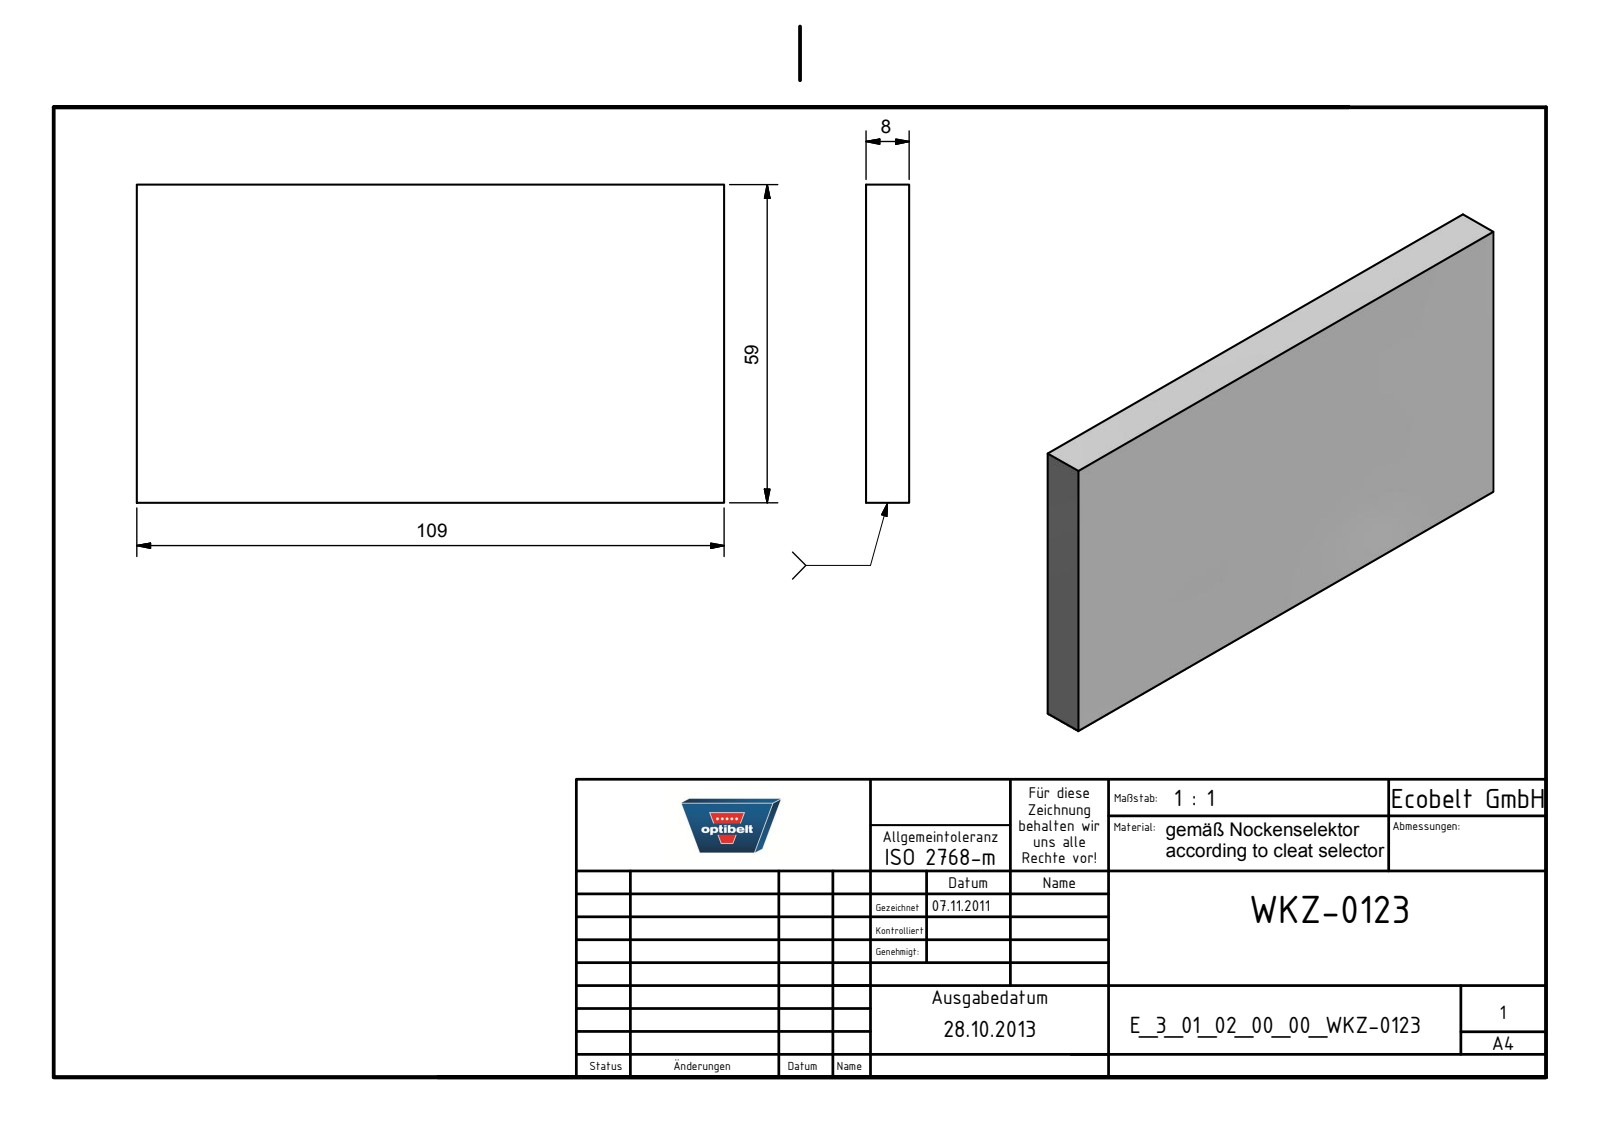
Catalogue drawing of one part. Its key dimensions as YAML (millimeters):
part_name: "E_3_01_02_00_00_WKZ-0123"
step_written_by: "Autodesk Inventor 2021 (AUTOMOTIVE_DESIGN)"
units: millimeters
bodies: {solids: 1, faces: 6, planar: 6, cylindrical: 0, other: 0}
overall_size: [109, 59, 8]
volume: 51448
surface_area: 15550
face_to_face_distances: [8, 59, 109]
